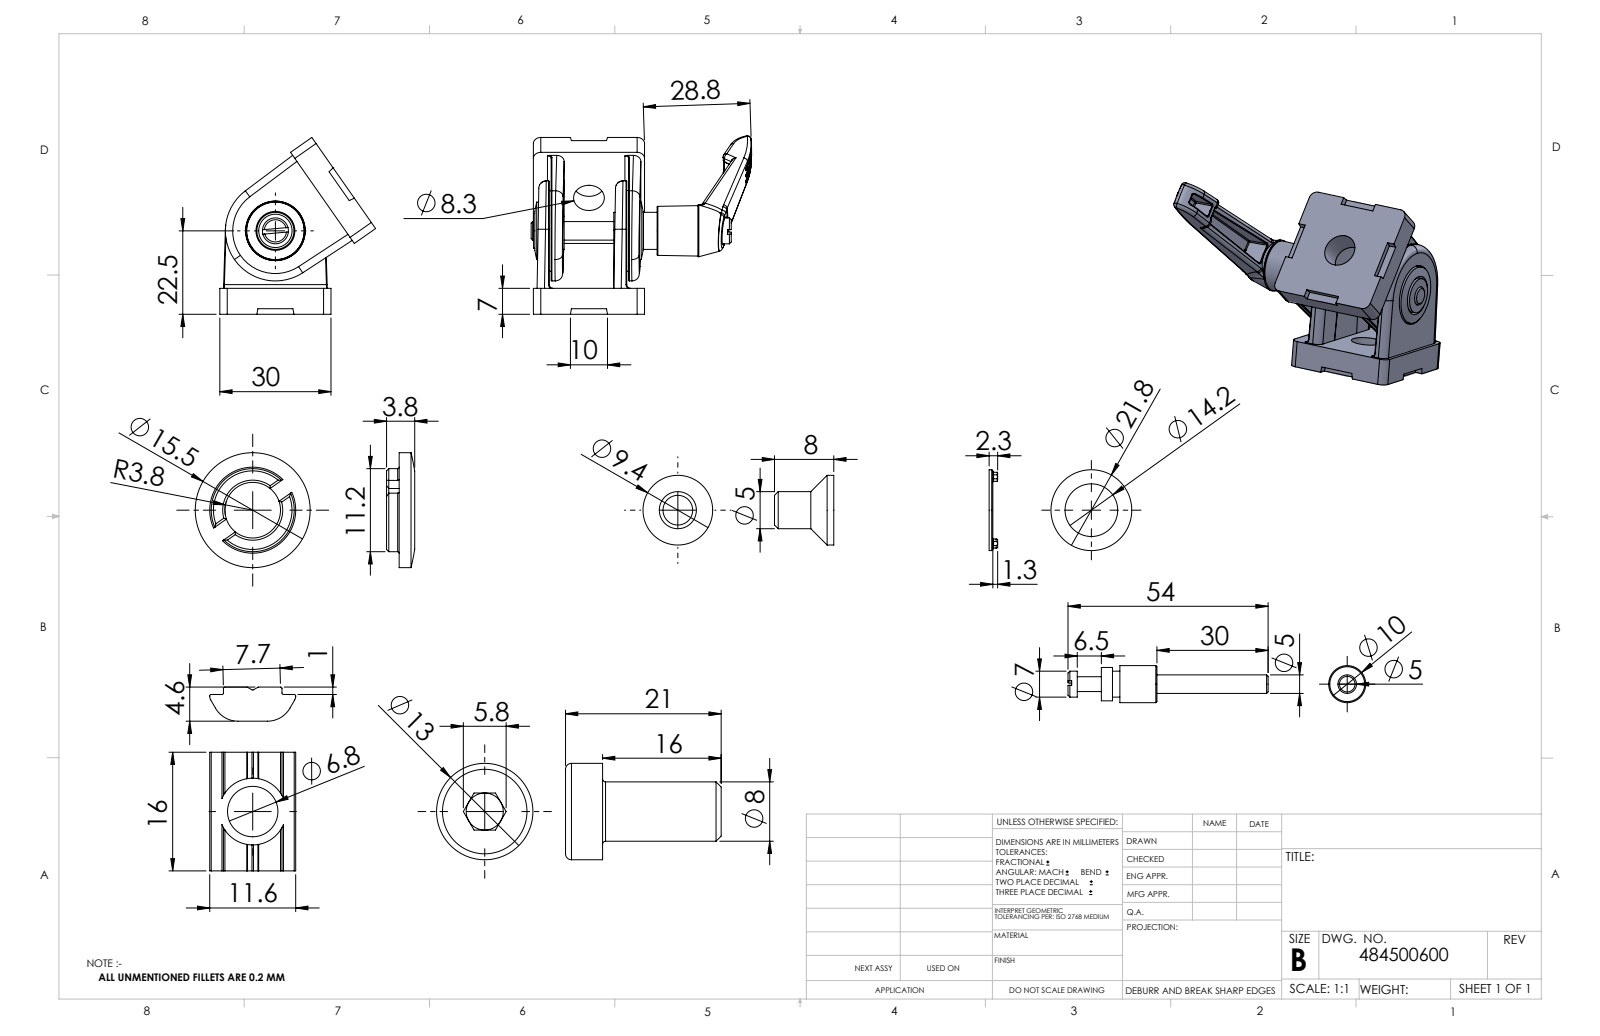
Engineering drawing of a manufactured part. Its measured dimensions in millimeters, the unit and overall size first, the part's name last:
Units: millimetres
Overall size (bounding box): 59.5 × 57.15 × 49.55
Round holes (diameter × count): ⌀2.5 ×4, ⌀6.8 ×2, ⌀4.2 ×1, ⌀7.5 ×1, ⌀14.2 ×1, ⌀22 ×1
Round bosses / shafts (diameter × count): ⌀13 ×2, ⌀8 ×2, ⌀27 ×1, ⌀21.8 ×1, ⌀15.5 ×1, ⌀14 ×1, ⌀11.2 ×1, ⌀10 ×1
Partial cylindrical surfaces — rounded edges, fillets, slot ends (radius × count): R0.2 ×36, R2 ×16, R0.3 ×8, R1 ×8, R1.23 ×4, R3.5 ×4, R0.25 ×3, R4.5 ×2
Main face-to-face distances: 0.5, 7, 20.4, 21.4, 20.9, 1, 19.9, 4.3, 4.8, 5.3
Hole centre spacings: 9, 8.31, 15.96, 17.99, 18
Bodies: 0 solids, 771 faces (243 planar, 201 cylindrical, 327 other)
Part name (STEP PRODUCT): 484500600_c_1
STEP written by: SolidWorks 2014 (CONFIG_CONTROL_DESIGN)
